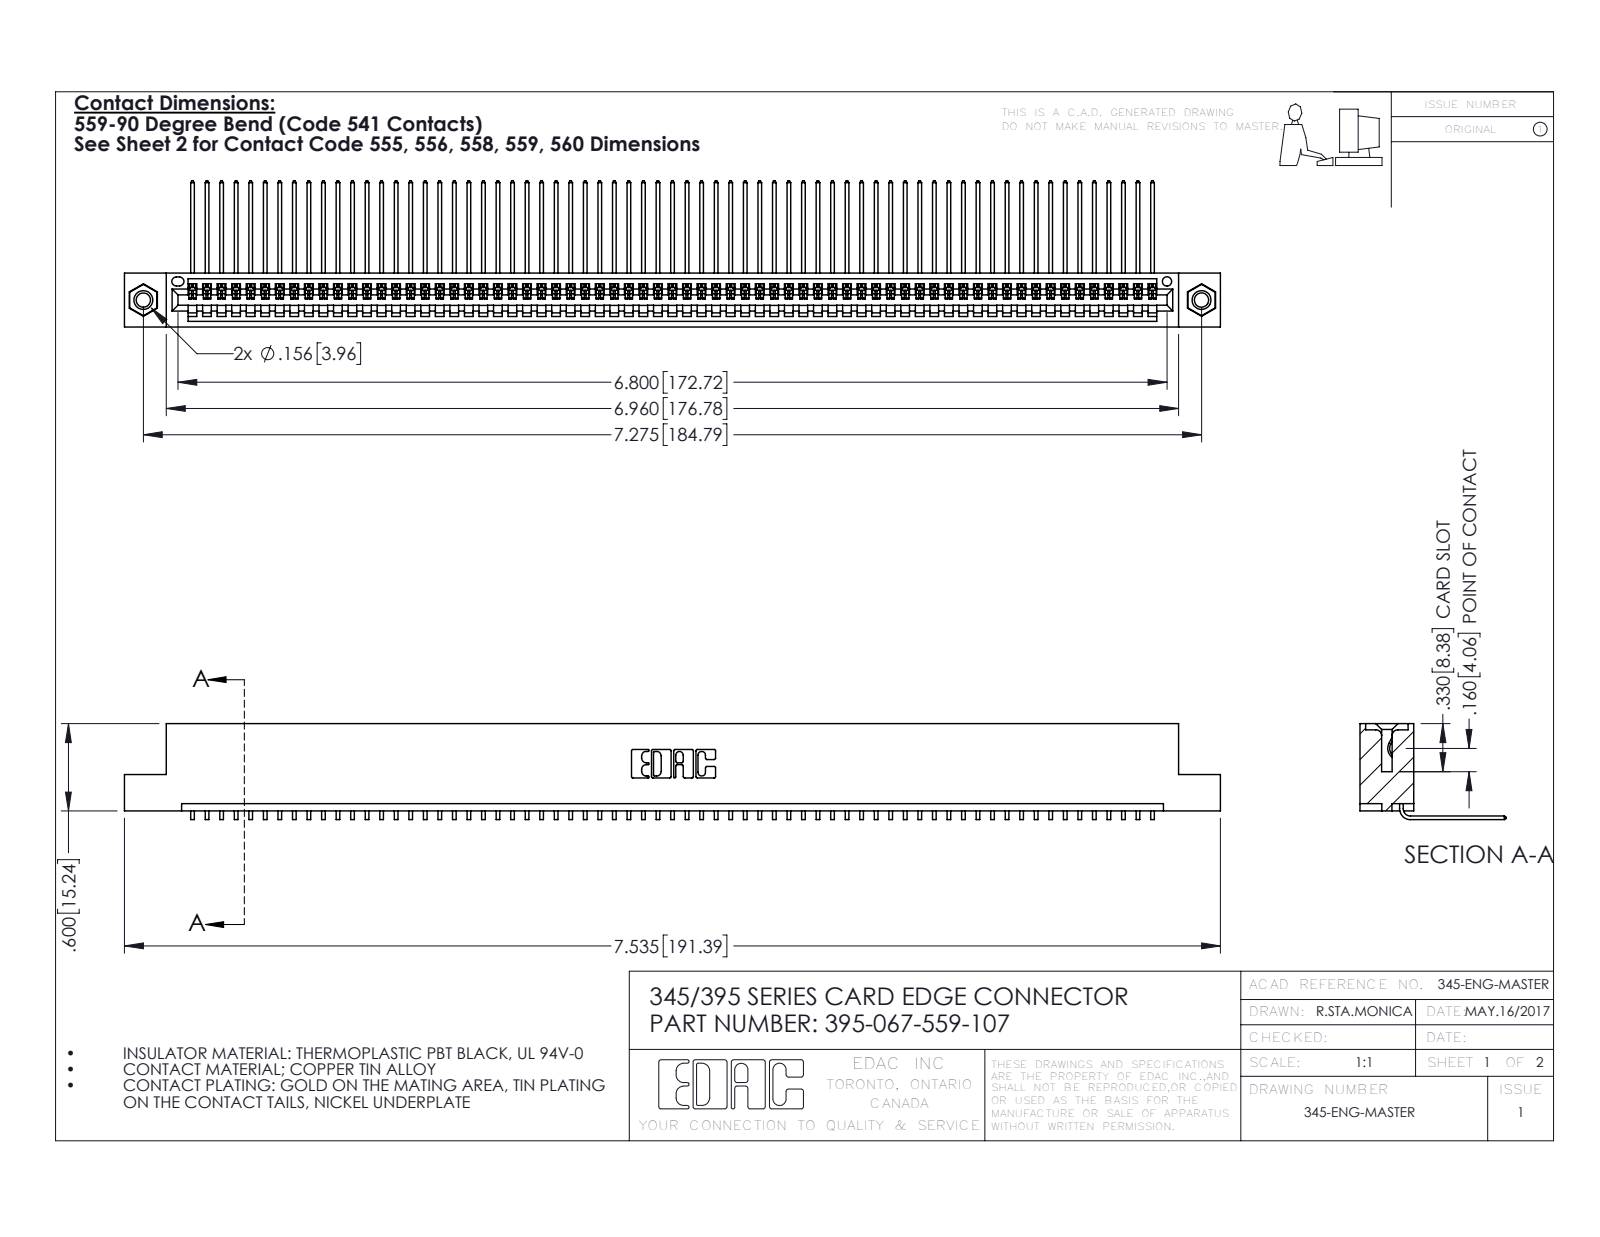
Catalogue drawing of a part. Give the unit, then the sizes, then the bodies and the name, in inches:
Units: inches
Overall size (bounding box): 7.535 × 1.005 × 0.659
Round holes (diameter × count): ⌀0.098 ×2, ⌀0.125 ×2, ⌀0.156 ×2, ⌀0.064 ×1
Round bosses / shafts (diameter × count): ⌀0.155 ×2
Partial cylindrical surfaces — rounded edges, fillets, slot ends (radius × count): R0.006 ×134, R0.01 ×22, R0.007 ×6, R0.031 ×6, R0.026 ×3, R0.031 ×2, R0.04 ×2, R0.014 ×1
Main face-to-face distances: 0.072, 0.298, 0.37, 0.2, 0.098, 0.272, 0.025, 0.225, 0.149, 0.072
Hole centre spacings: 0.27, 7.039, 7.275
Volume: 1.135 in³ · Surface area: 40.91 in²
Bodies: 70 solids, 4206 faces (2926 planar, 1264 cylindrical, 16 other)
Part name (STEP PRODUCT): 395-067-559-107; 345 Part_Flush Mounting Lugs - 0.156 Dia-TI; 345-292-001_558 559 Tail - 1; 345-250-001_345-250-005-103
STEP written by: SolidWorks 2016 (CONFIG_CONTROL_DESIGN)
